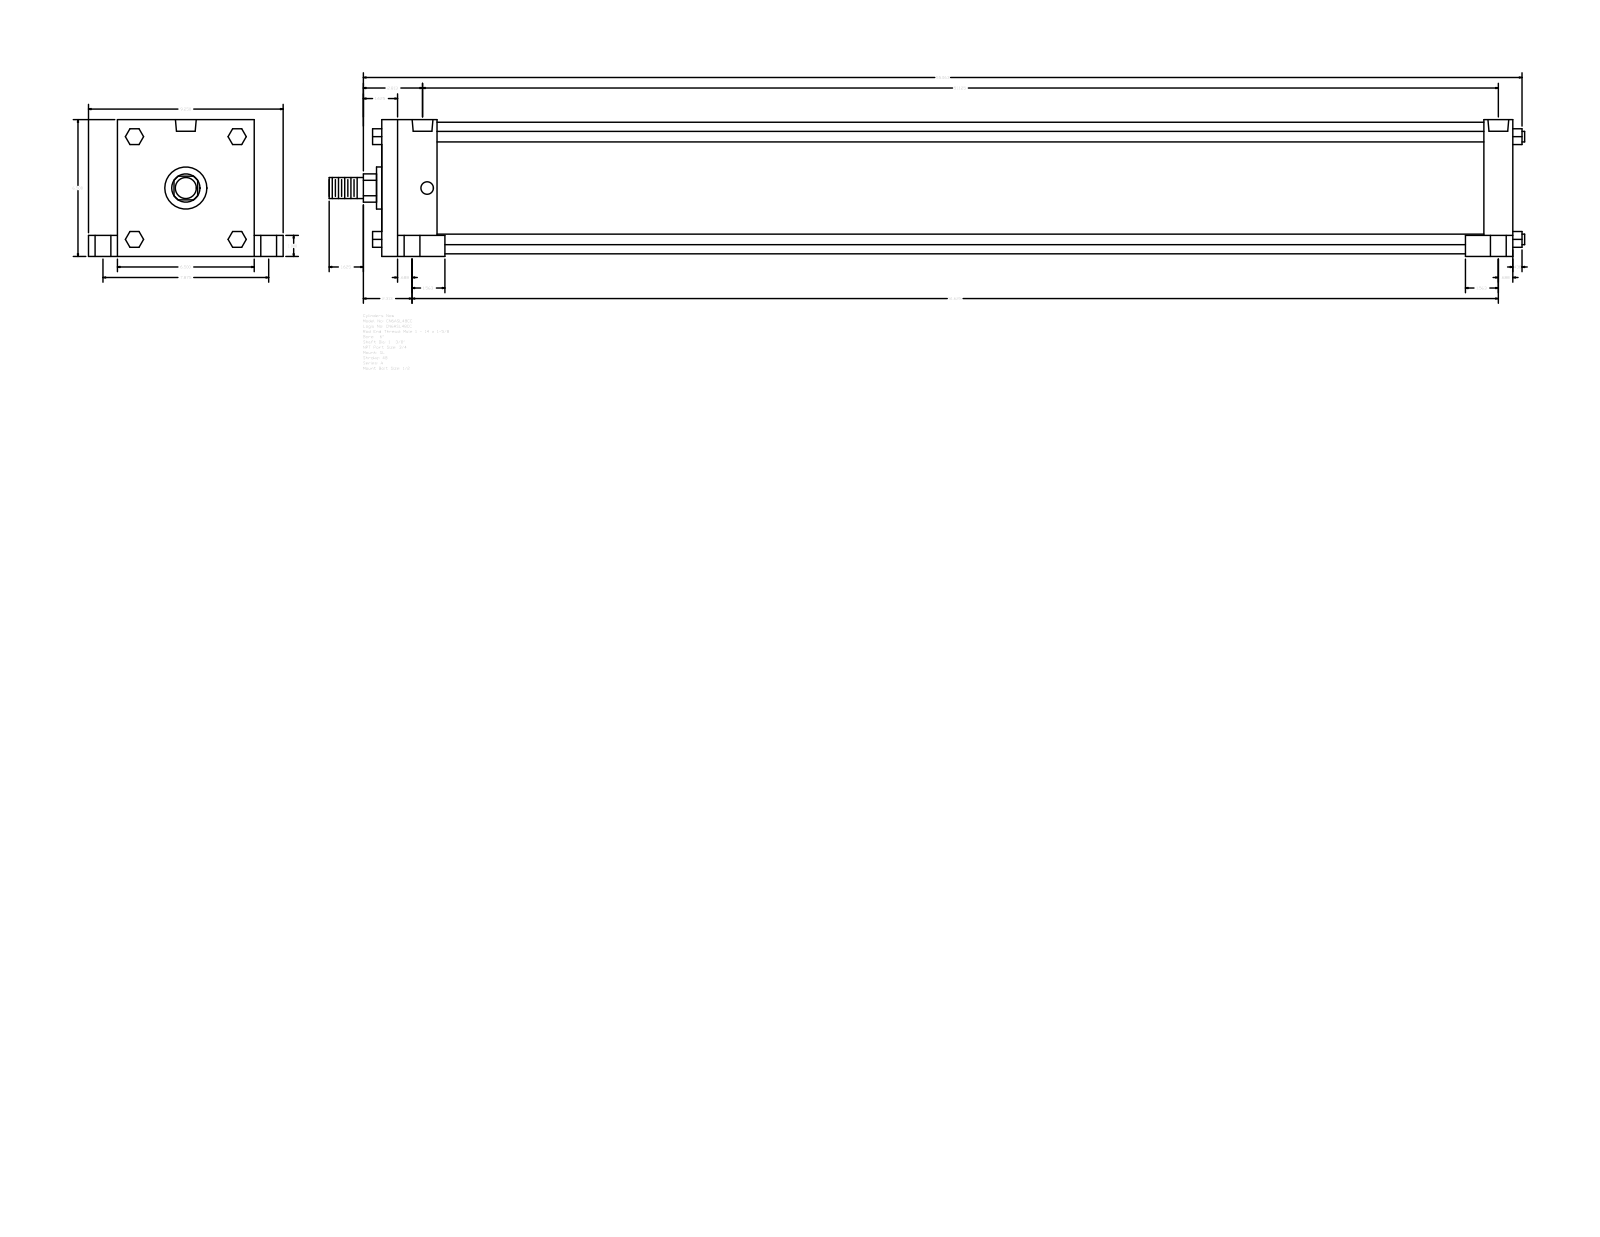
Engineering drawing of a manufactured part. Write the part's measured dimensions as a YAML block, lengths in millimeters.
part_name: "A_SL__0600_1.375"
step_written_by: "GSSL Pune (CONFIG_CONTROL_DESIGN)"
units: millimeters
bodies: {solids: 0, faces: 150, planar: 114, cylindrical: 36, other: 0}
overall_size: [1443.04, 234.95, 165.1]
round_holes:
  - {diameter: 15.08, count: 4}
  - {diameter: 19.05, count: 4}
  - {diameter: 25.4, count: 4}
  - {diameter: 25.12, count: 2}
round_bosses_or_shafts:
  - {diameter: 12.7, count: 4}
  - {diameter: 158.75, count: 1}
  - {diameter: 50.8, count: 1}
  - {diameter: 34.92, count: 1}
  - {diameter: 25.4, count: 1}
partial_cylinders:
  - {radius: 17.06, count: 1}
face_to_face_distances: [165.1, 1365.24, 34.92, 66.67, 1298.57, 1330.32, 1263.65, 25.4, 139.7, 200.02]
hole_center_spacings: [5.56, 100.01, 100.16, 100.81, 101.66, 200.02, 1287.45, 1293.01]
